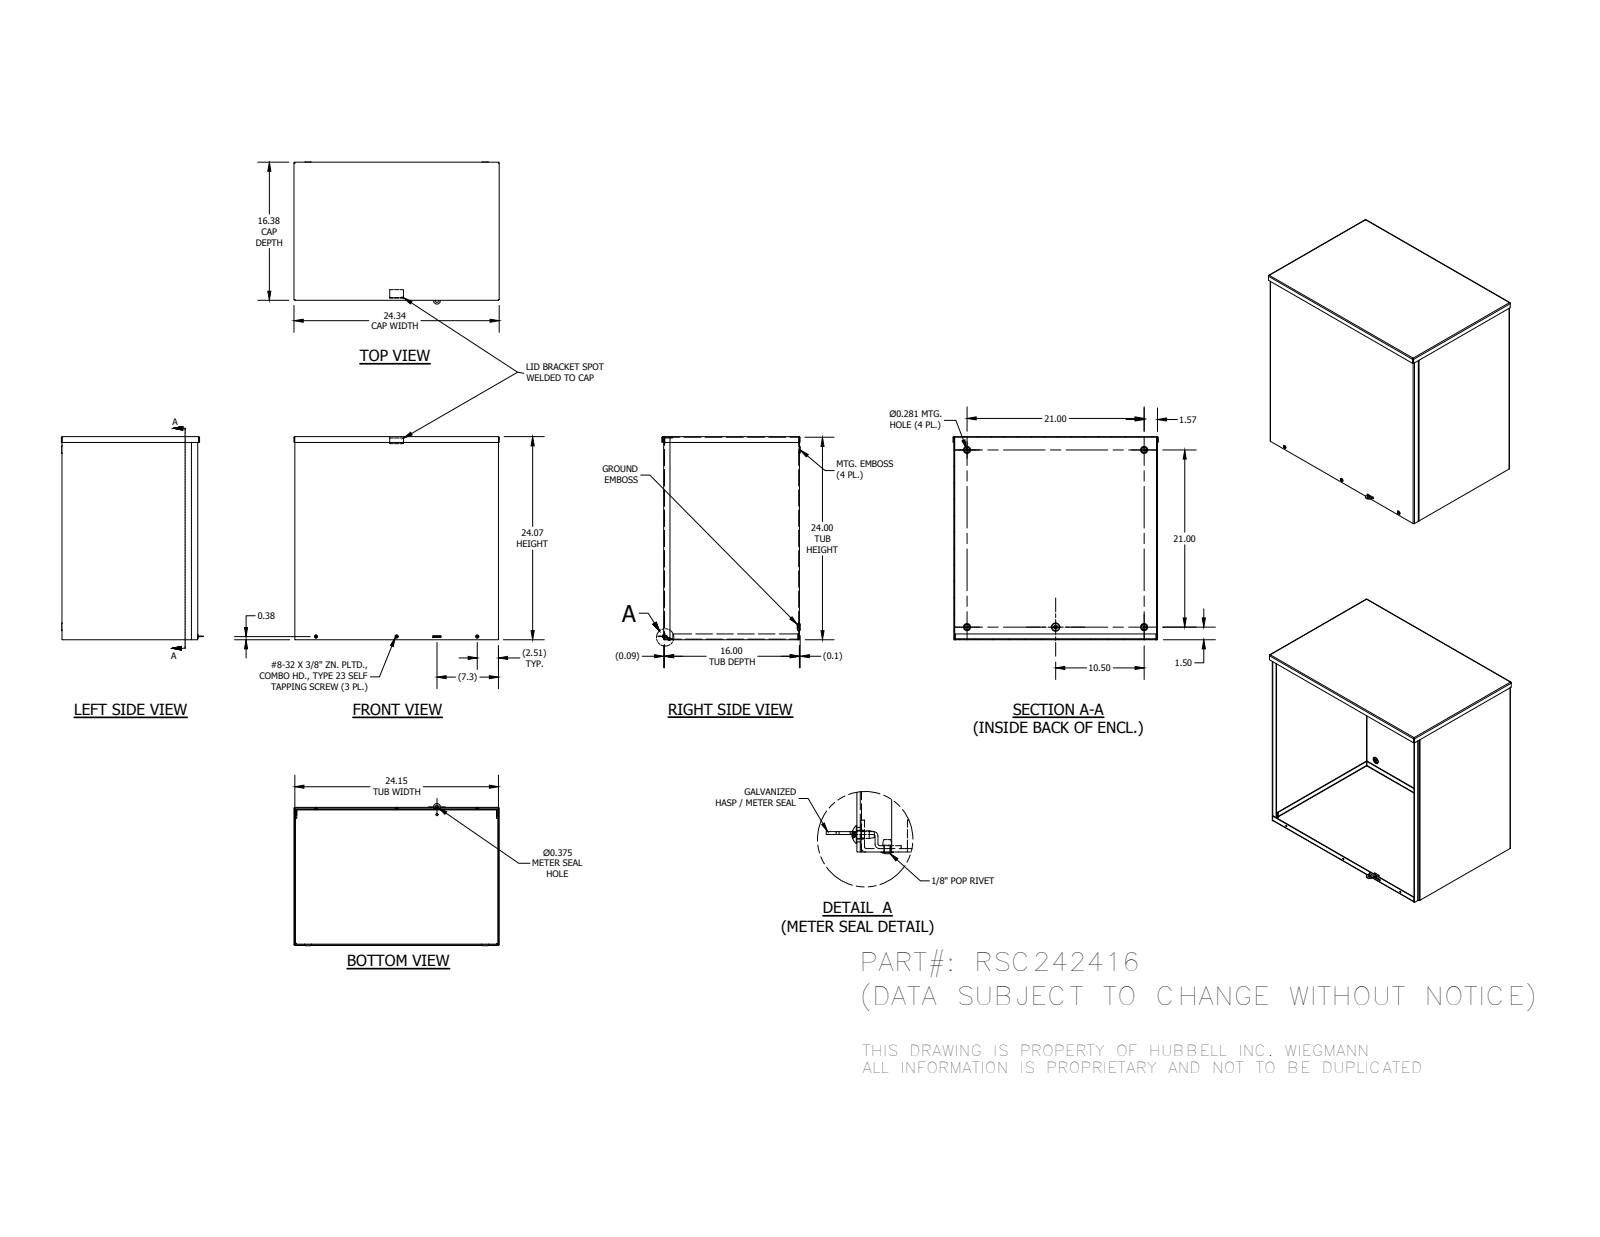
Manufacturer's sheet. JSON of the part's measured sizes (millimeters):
{"part_name": "RSC242416BKPA; RSC2416EWPA; RSC2424LFA; RSC2416CPA (+5 more)", "step_written_by": "Autodesk Inventor 2014 (AUTOMOTIVE_DESIGN)", "units": "millimeters", "bodies": {"solids": 10, "faces": 350, "planar": 193, "cylindrical": 66, "other": 91}, "overall_size": [618.12, 612.5, 428], "volume_mm3": 3434000, "surface_area_mm2": 3677000, "round_holes": [[7.94, 6], [7.14, 4], [3.73, 3], [3.17, 1], [3.45, 1], [4.34, 1], [9.52, 1]], "round_bosses_or_shafts": [[9.75, 3], [4.17, 3], [6.65, 1], [5.93, 1], [3.17, 1]], "partial_cylinders_radius": [[0.79, 19], [2.67, 17], [2.37, 2], [10.16, 1]], "face_to_face_distances": [1.88, 609.6, 406.8, 611.48, 408.68, 404.92, 607.72, 613.36, 3.94, 607.54], "hole_center_spacings": [242.89, 268.23, 510.39, 533.4, 638.55, 590.55, 37.19, 37.2]}
